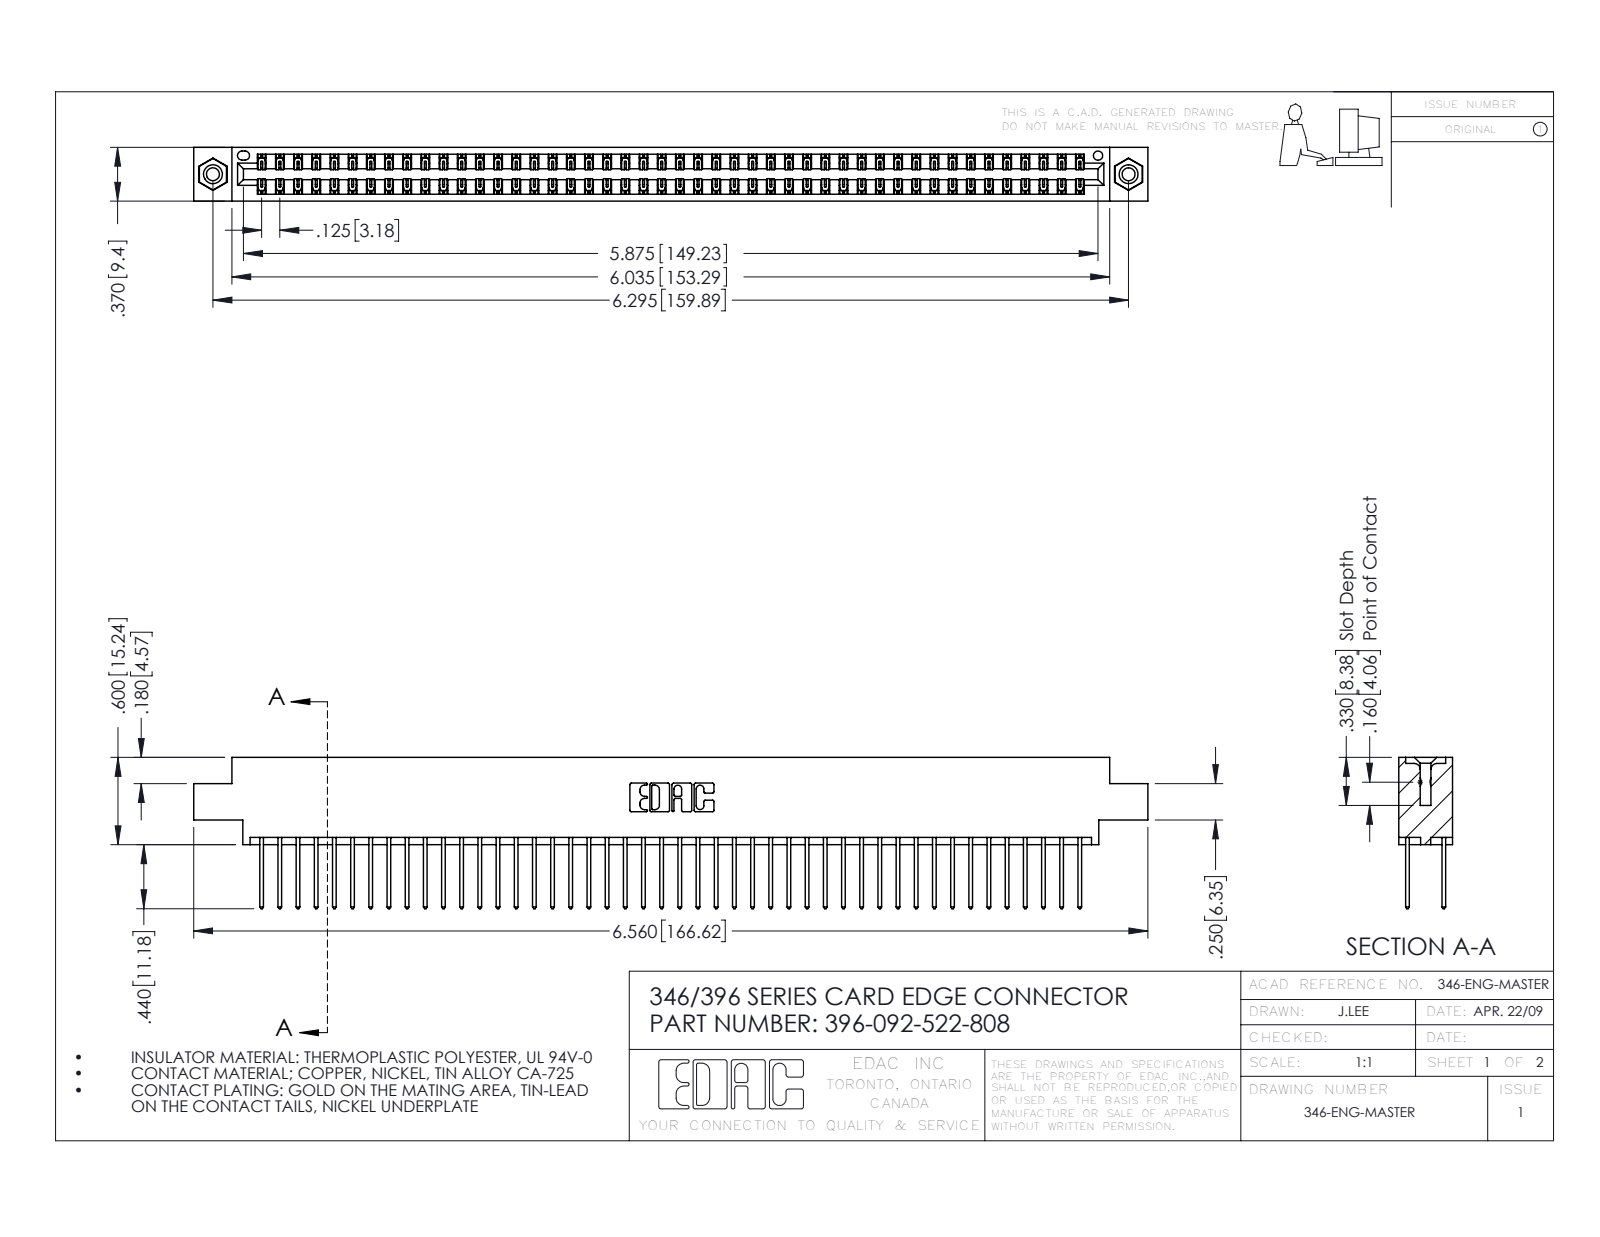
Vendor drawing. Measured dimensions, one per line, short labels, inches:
name: 396-092-522-808; 345-250-001_345-250-003-102; 345-292-001_345-293-122; 346 Part_0.170 Offset - 0.156 Dia-TI
written by: SolidWorks 2016 (CONFIG_CONTROL_DESIGN)
unit: in
bodies: 95 solids, 4970 faces (3332 planar, 1622 cylindrical, 16 other)
size: 6.56 × 1.04 × 0.37
volume: 0.998 in³; area: 36.94 in²
holes: 2× ⌀0.089, 2× ⌀0.125, 2× ⌀0.156, 1× ⌀0.064
bosses: 2× ⌀0.155
rounds: 138× R0.006, 92× R0.01, 22× R0.01, 6× R0.007, 6× R0.031, 3× R0.026, 2× R0.014, 2× R0.022
face distances: 0.048, 0.322, 0.25, 0.37, 0.072, 0.298, 0.025, 0.275, 0.222, 0.148
hole spacings: 0.246, 6.086, 6.295
